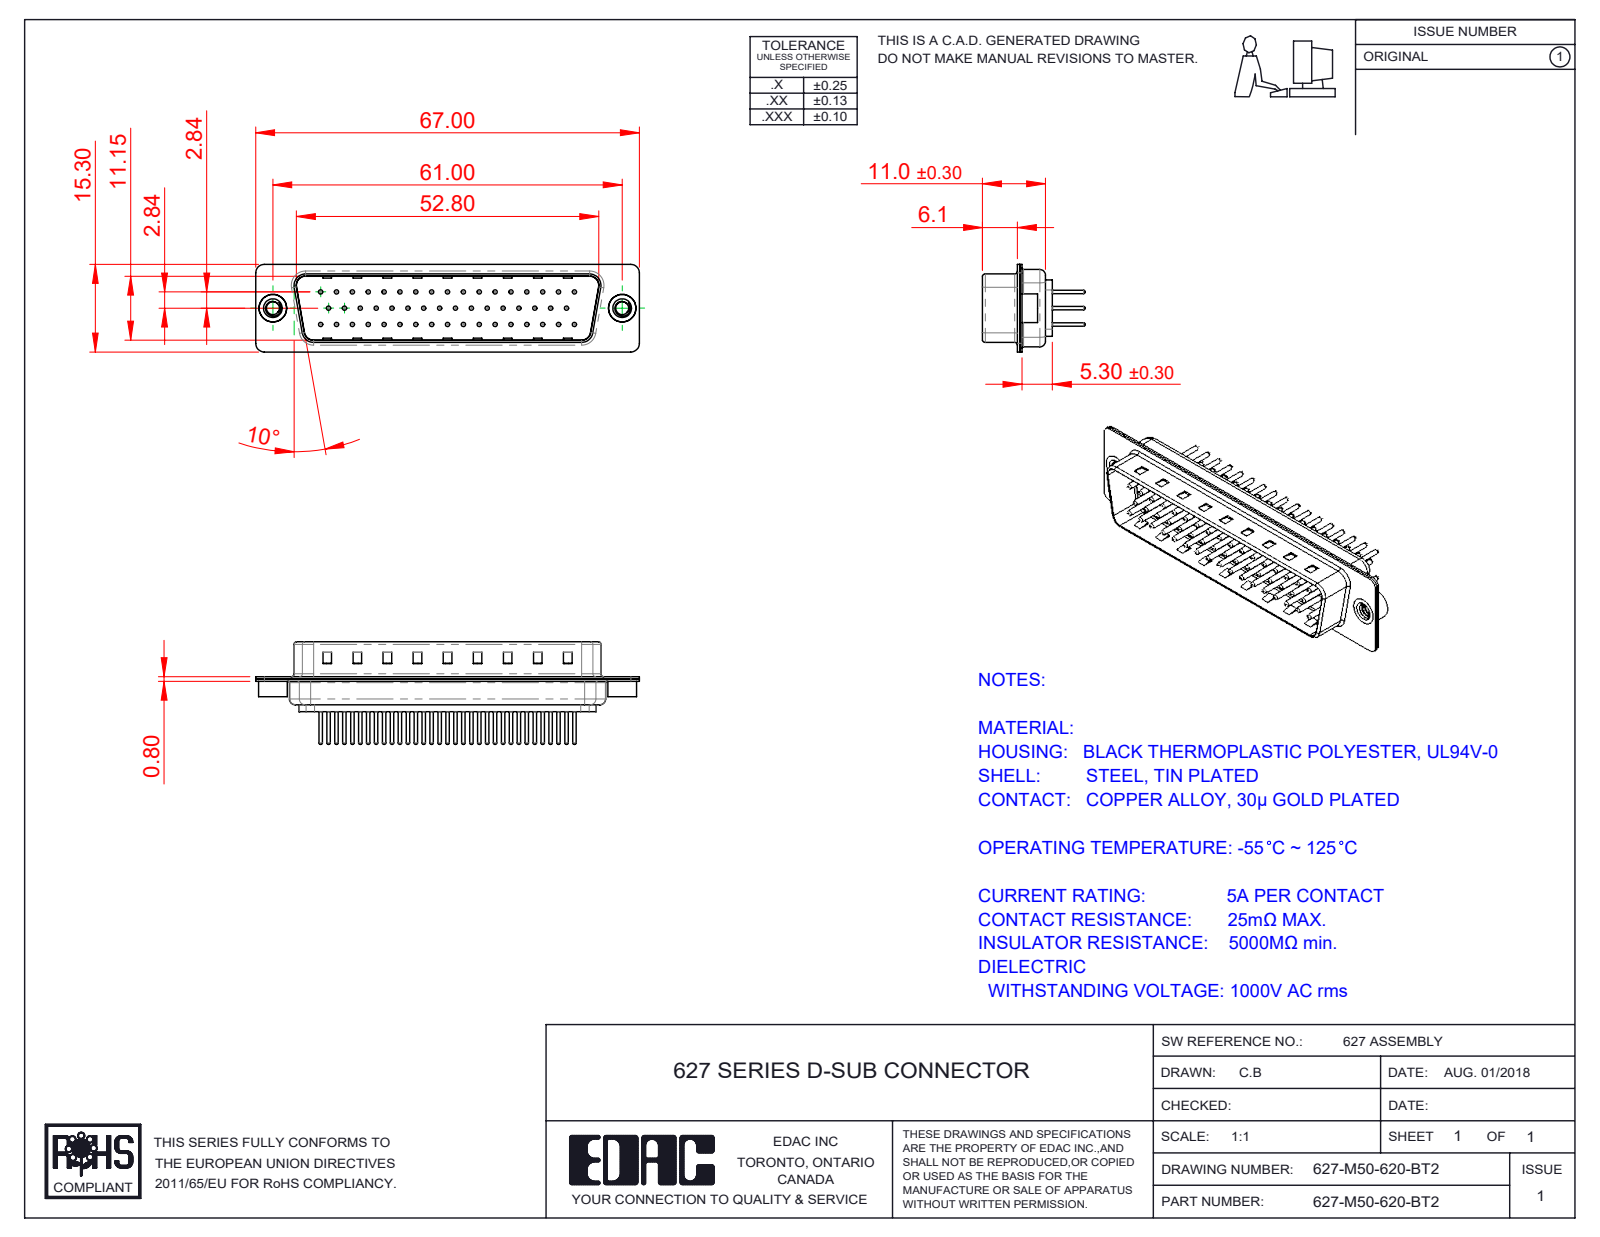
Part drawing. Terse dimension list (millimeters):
name: 627M 4-40 Threaded Rivet; 627M Contact Row 3_20; 627M Shell Front_50 Contacts; 627M Contact Row 1_20 (+4 more)
written by: SolidWorks 2020 (CONFIG_CONTROL_DESIGN)
unit: mm
bodies: 55 solids, 2262 faces (553 planar, 841 cylindrical, 868 other)
size: 67 × 17.9 × 15.3
volume: 4 525 mm³; area: 10 699 mm²
holes: 50× ⌀0.75, 50× ⌀1.6, 50× ⌀2, 2× ⌀2.26, 2× ⌀4, 2× ⌀4.8
bosses: 50× ⌀1.5, 50× ⌀0.6, 2× ⌀5, 2× ⌀4.9
rounds: 16× R1.5, 12× R2, 8× R0.5, 8× R1.6, 4× R0.25, 4× R0.6, 4× R0.65, 4× R0.9
face distances: 0.4, 11.55, 5.7, 6.1, 0.78, 0.77, 12.33, 12.32, 13.1, 5.3
hole spacings: 3.16, 2.77, 5.54, 8.31, 11.08, 13.85, 16.62, 5.03
